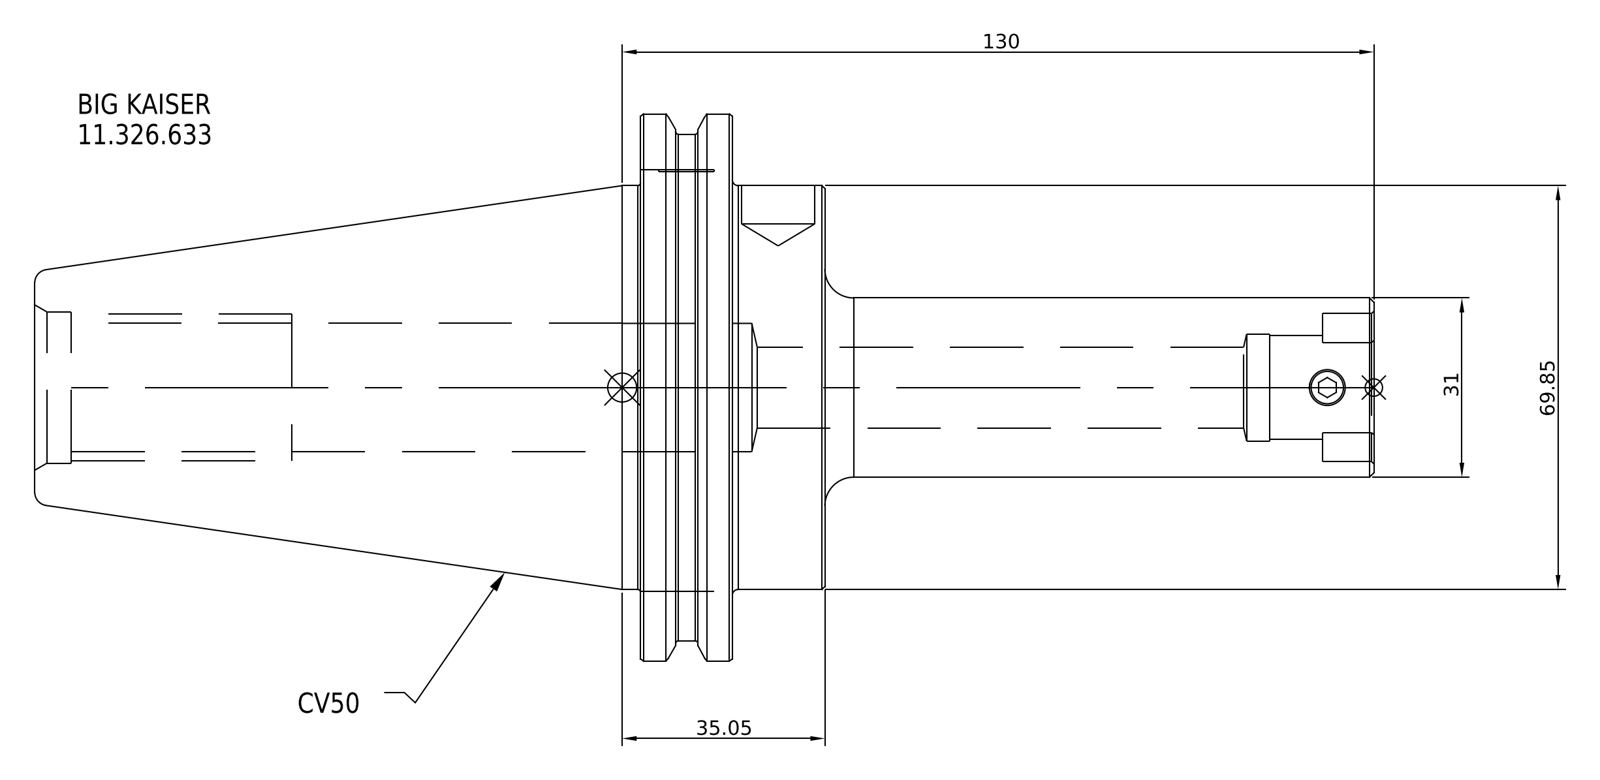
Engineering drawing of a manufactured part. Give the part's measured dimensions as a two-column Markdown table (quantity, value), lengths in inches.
| quantity | value |
| --- | --- |
| part name | 11.326.633 |
| STEP written by | SolidWorks 2021 (CONFIG_CONTROL_DESIGN) |
| units | inches |
| bodies | 1 solid, 16 faces (7 planar, 6 cylindrical, 3 other) |
| overall size | 9.118 × 3.875 × 3.875 |
| volume | 31.38 in³ |
| surface area | 77.85 in² |
| round bosses / shafts (diameter × count) | 3.875 × 1, 3.594 × 1, 2.75 × 1, 1.22 × 1 |
| main face-to-face distances | 0.691, 0.628, 1.319, 5.378, 4.75, 4.059, 3.74, 4.368, 5.059, 9.118 |
